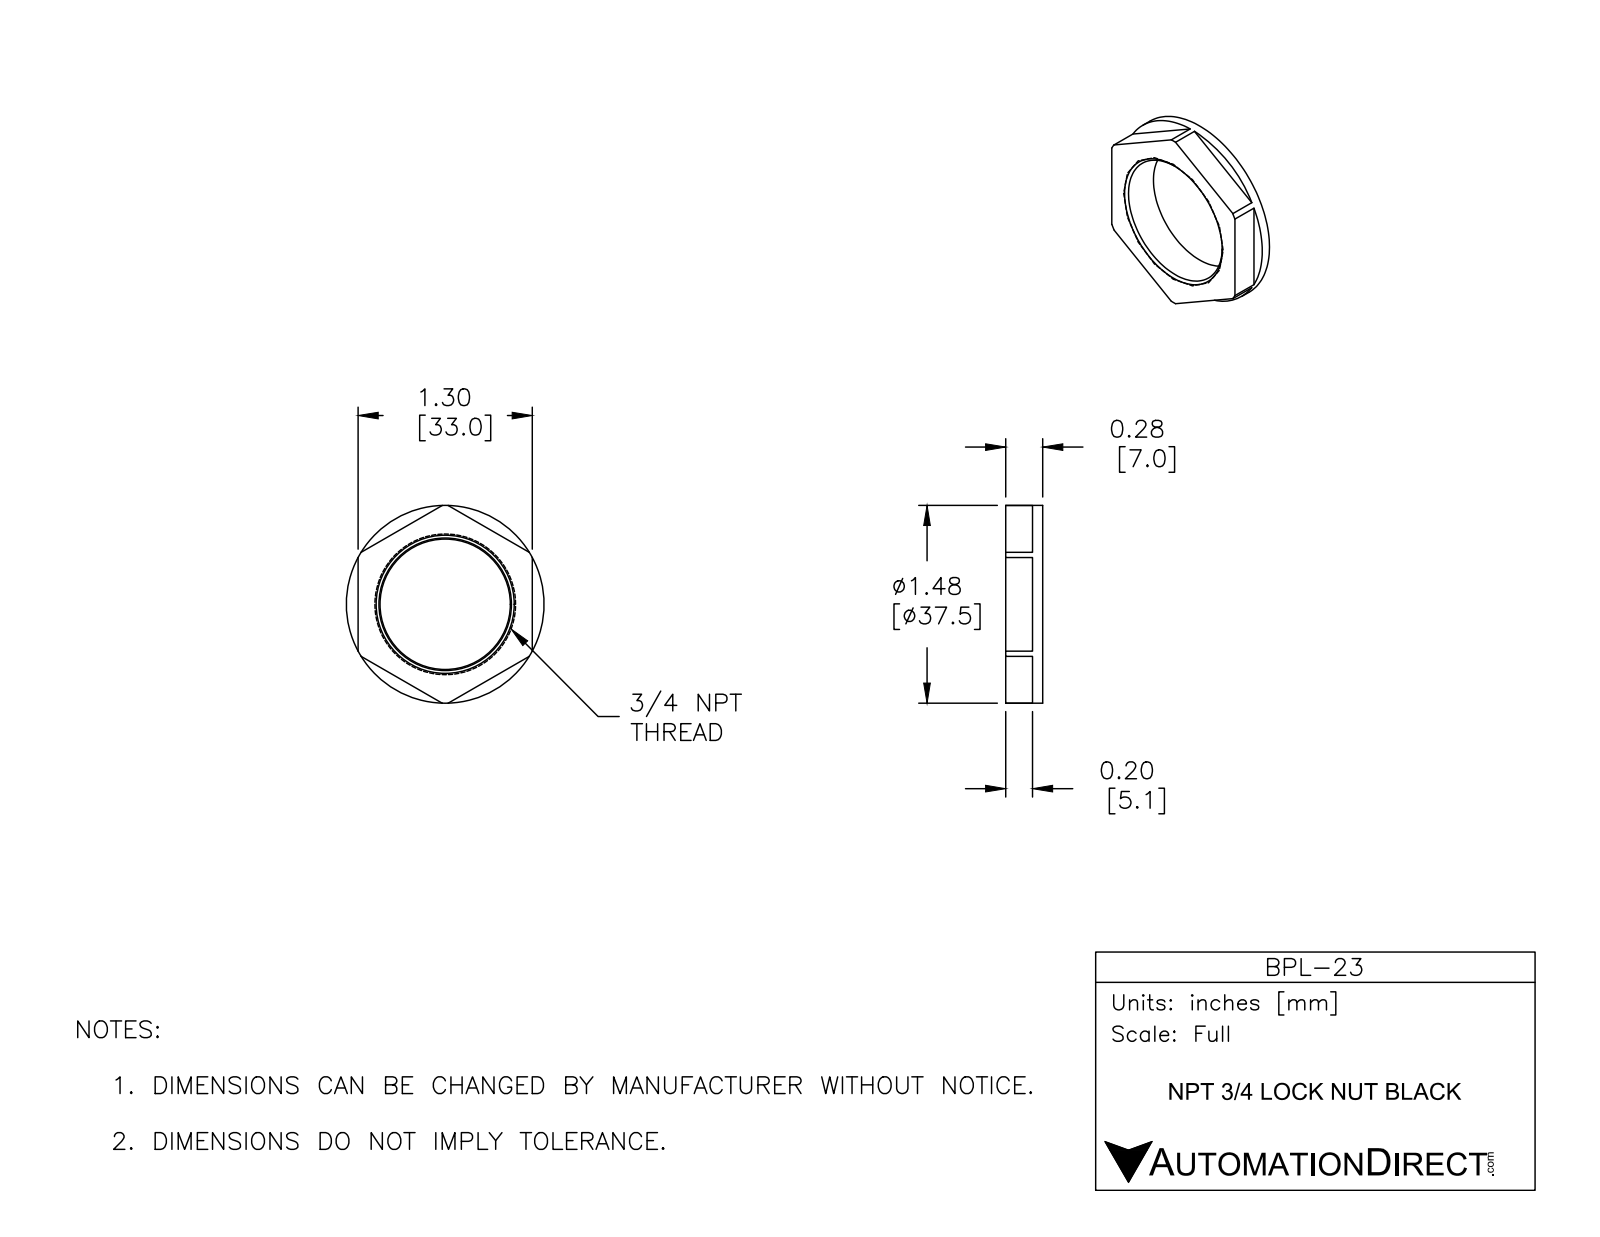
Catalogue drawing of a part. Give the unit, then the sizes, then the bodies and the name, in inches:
Units: inches
Overall size (bounding box): 1.476 × 1.476 × 0.276
Round bosses / shafts (diameter × count): ⌀1.476 ×1
Main face-to-face distances: 0.276, 1.3, 0.076, 0.2
Volume: 0.186 in³ · Surface area: 3.818 in²
Bodies: 1 solid, 20 faces (14 planar, 2 cylindrical, 4 other)
Part name (STEP PRODUCT): BPL-23
STEP written by: SolidWorks 2015 (CONFIG_CONTROL_DESIGN)
